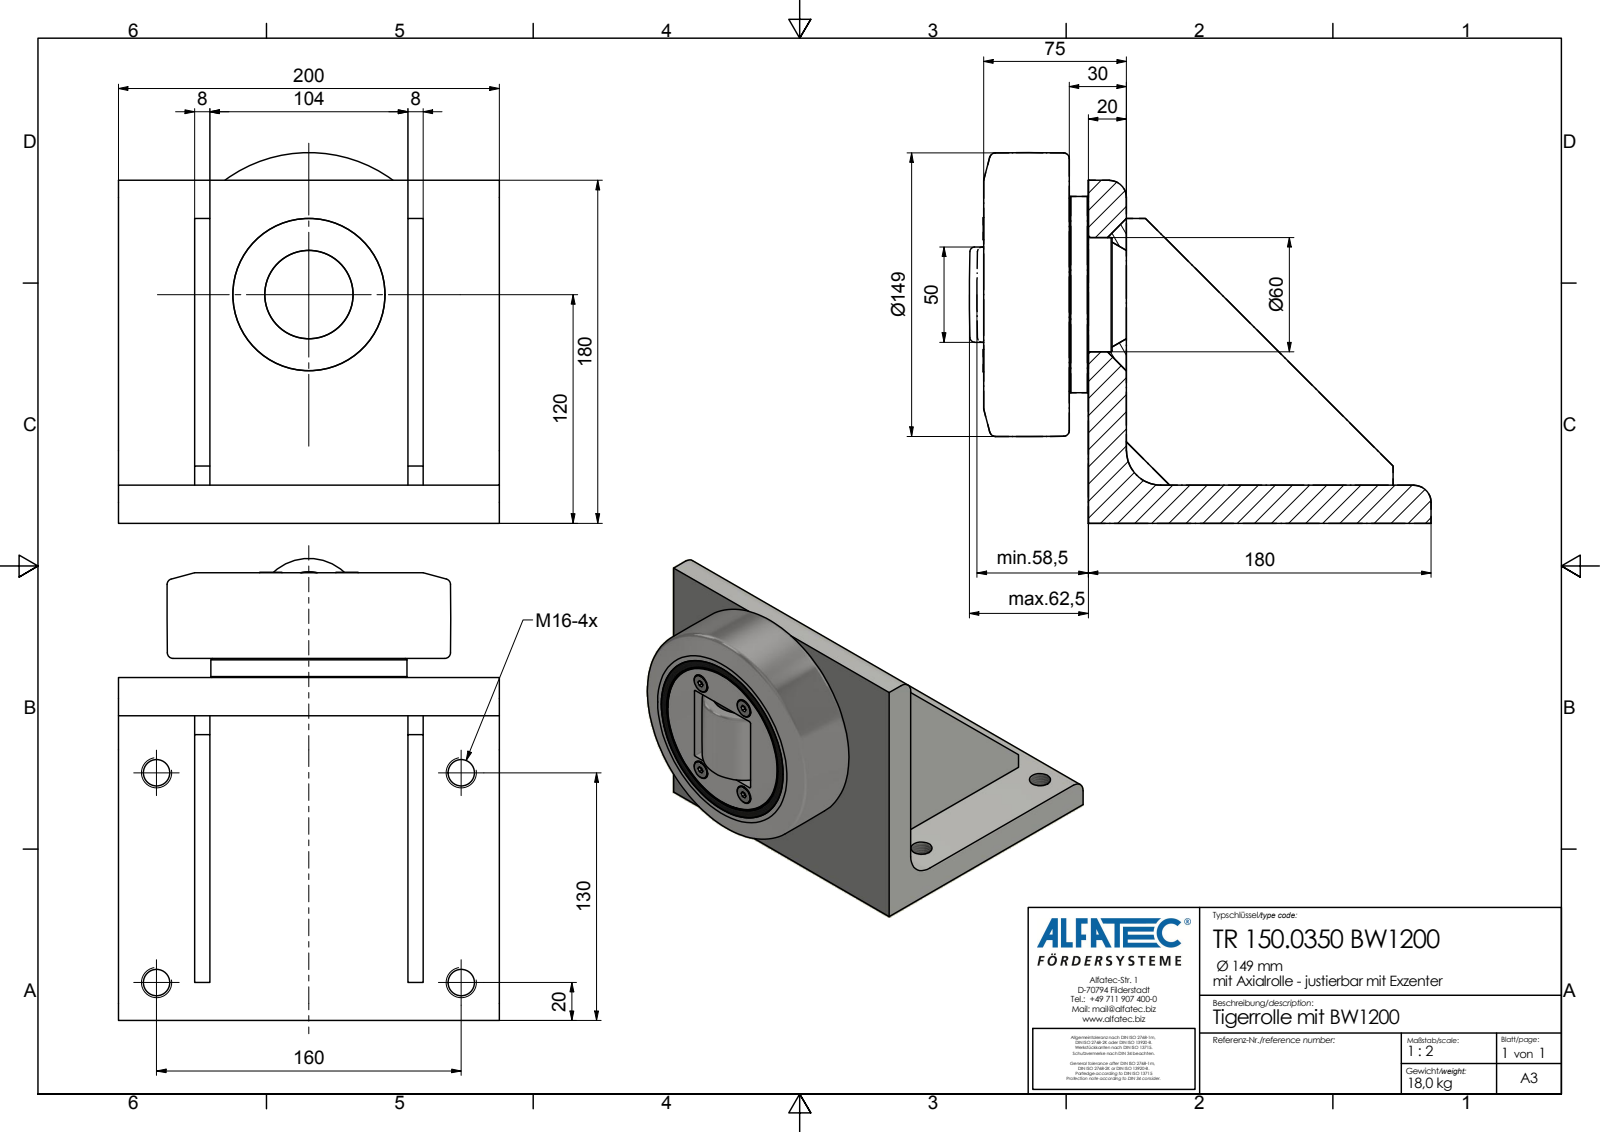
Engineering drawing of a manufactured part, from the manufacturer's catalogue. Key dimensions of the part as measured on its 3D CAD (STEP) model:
Part name (STEP PRODUCT): TR 150.0350 BW1200_Kontur
STEP written by: Autodesk Inventor 2020 (AP242_MANAGED_MODEL_BASED_3D_ENGINEERING_MIM_LF)
Units: millimetres
Bodies: 1 solid, 87 faces (61 planar, 17 cylindrical, 9 other)
Overall size (bounding box): 242.49 × 200 × 194.5
Volume: 2 392 000 mm³ · Surface area: 241 734 mm²
Round holes (diameter × count): ⌀13.84 ×4
Round bosses / shafts (diameter × count): ⌀11.7 ×4, ⌀103 ×1, ⌀101.4 ×1
Partial cylindrical surfaces — rounded edges, fillets, slot ends (radius × count): R9 ×2, R18 ×1, R20.4 ×1, R20.5 ×1
Main face-to-face distances: 20, 8, 112, 160, 40, 48, 152, 104, 120, 75
Hole centre spacings: 110, 160, 194.16
